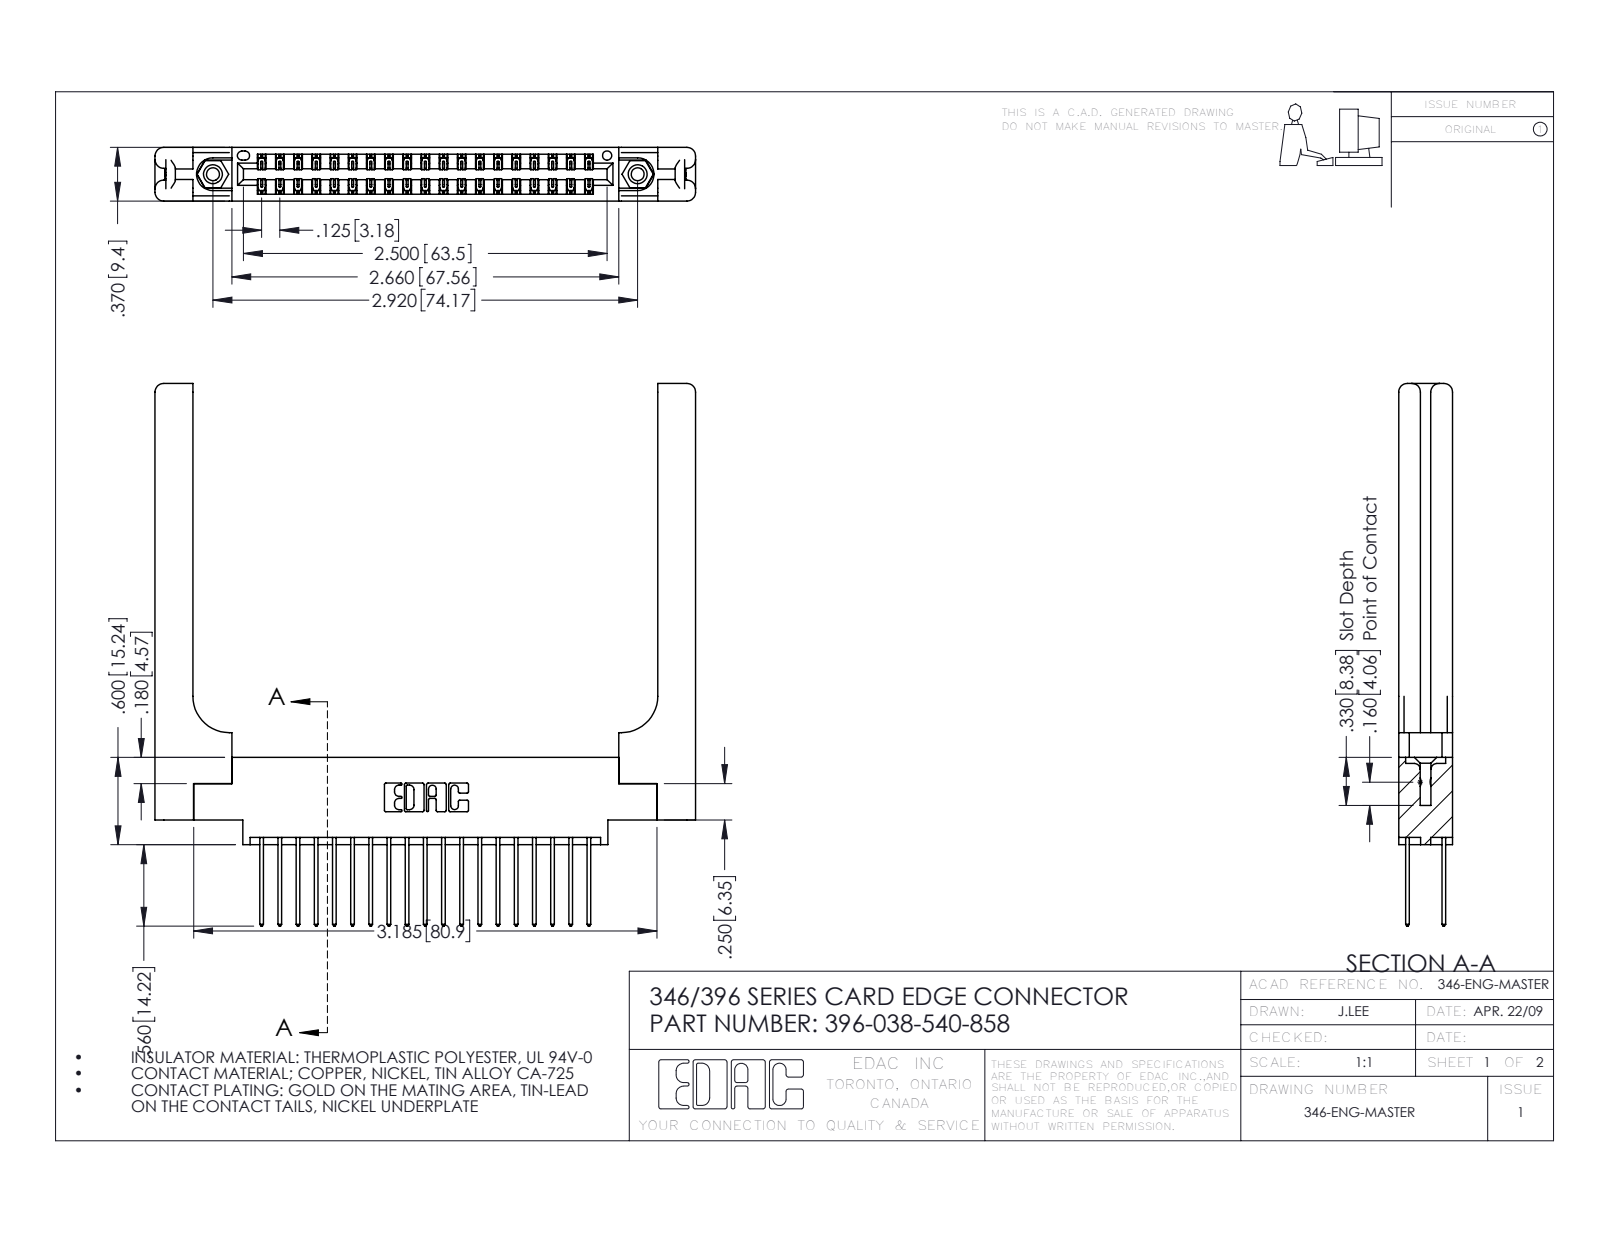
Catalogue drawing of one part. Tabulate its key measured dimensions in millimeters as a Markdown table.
| quantity | value |
| --- | --- |
| part name | 346 Part_0.170 Offset - 0.156 Dia-TH; 345-292-001_345-293-140; 396-038-540-858; 346-220-058_345-220-058 (+1 more) |
| STEP written by | SolidWorks 2016 (CONFIG_CONTROL_DESIGN) |
| units | millimeters |
| bodies | 43 solids, 2358 faces (1558 planar, 740 cylindrical, 60 other) |
| overall size | 94.7 × 94.4 × 9.4 |
| volume | 16 500 mm³ |
| surface area | 17 860 mm² |
| round holes (diameter × count) | 2.3 × 2, 3.2 × 2, 4 × 2, 1.6 × 1 |
| round bosses / shafts (diameter × count) | 3.9 × 2 |
| partial cylindrical surfaces (radius × count) | 0.2 × 57, 0.3 × 38, 0.3 × 22, 1.5 × 16, 0.2 × 6, 0.8 × 6, 0.7 × 3, 0.4 × 2 |
| main face-to-face distances | 9.4, 1.8, 1.2, 8.2, 3.8, 3.8, 6.4, 0.6, 7.6, 7 |
| hole center spacings | 6.2, 68.9, 74.2 |
